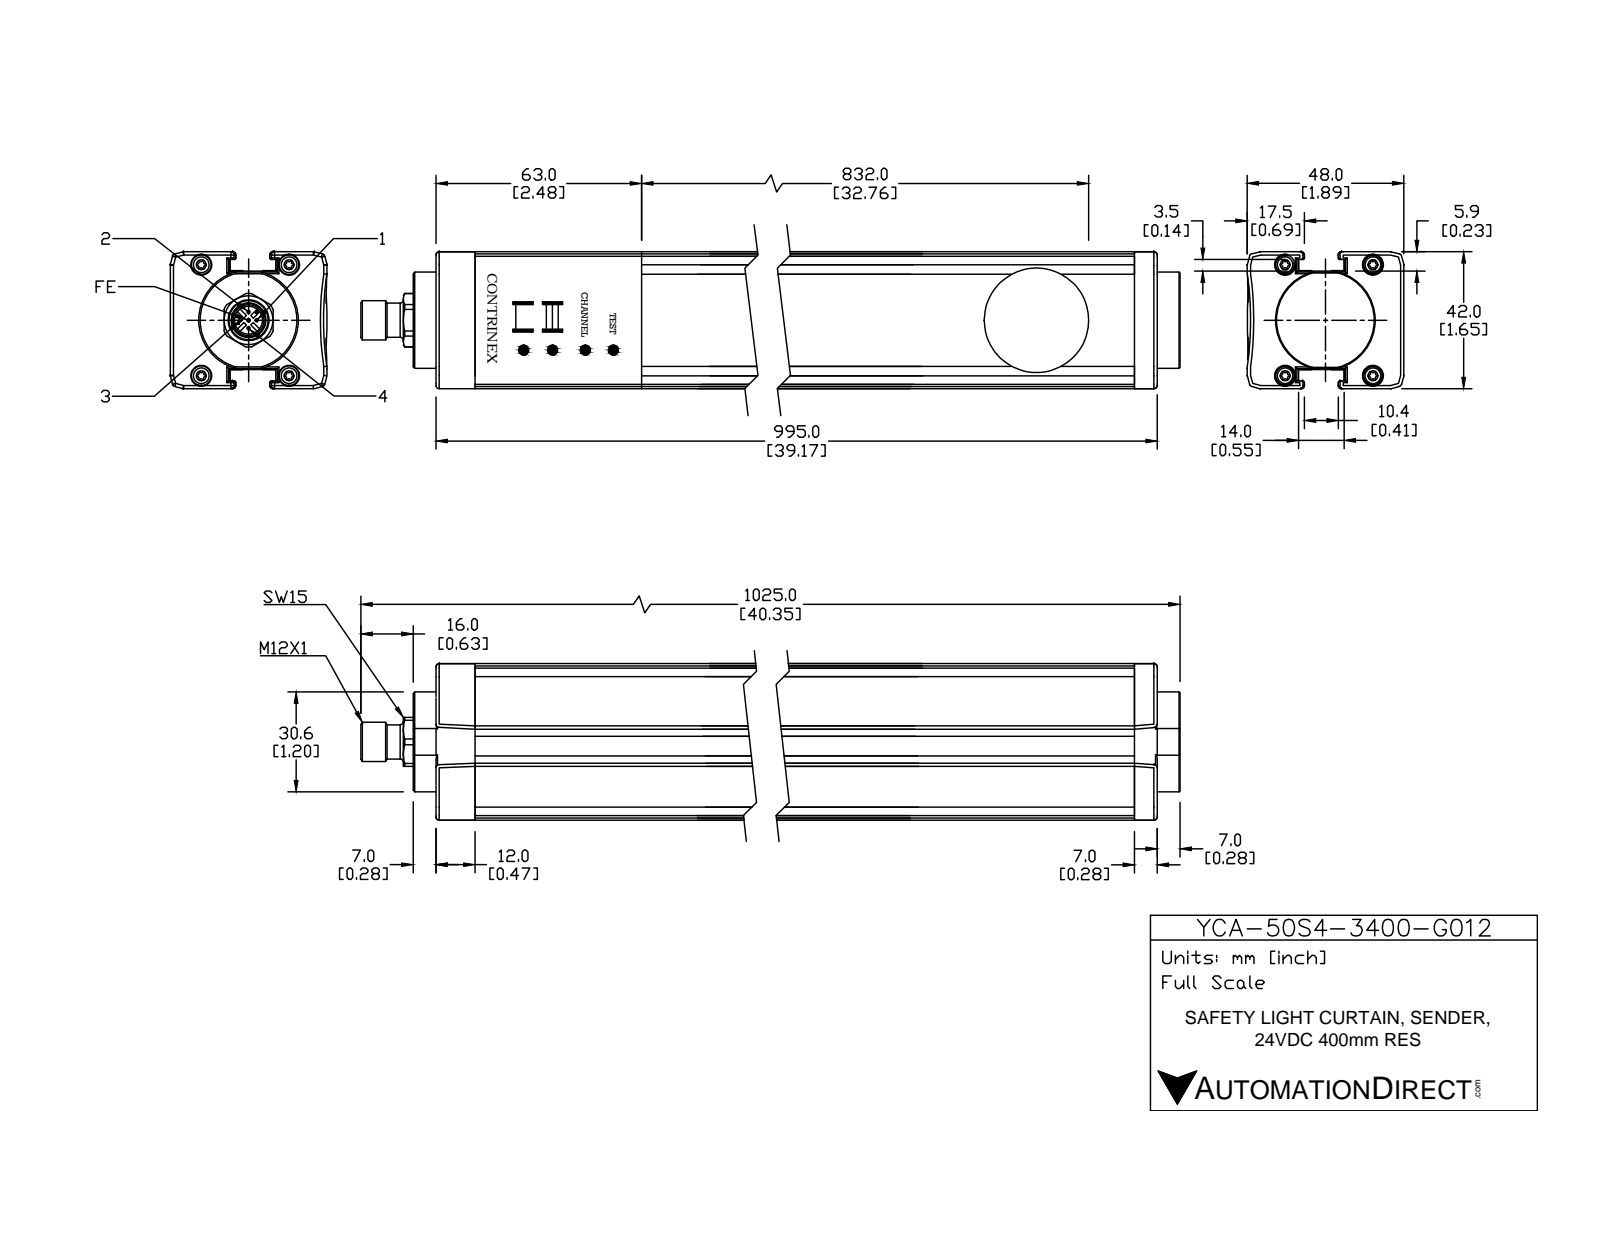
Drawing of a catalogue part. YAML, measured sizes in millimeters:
part_name: "YCA-50S4-3400-G012"
step_written_by: "SolidWorks 2016 (AUTOMOTIVE_DESIGN)"
units: millimeters
bodies: {solids: 18, faces: 454, planar: 221, cylindrical: 172, other: 61}
overall_size: [1025, 48, 42]
volume: 1794000
surface_area: 231840
round_holes:
  - {diameter: 6, count: 4}
  - {diameter: 1, count: 1}
  - {diameter: 8.5, count: 1}
  - {diameter: 32, count: 1}
round_bosses_or_shafts:
  - {diameter: 5.5, count: 4}
  - {diameter: 1, count: 4}
  - {diameter: 30.6, count: 1}
  - {diameter: 12, count: 1}
  - {diameter: 10.5, count: 1}
partial_cylinders:
  - {radius: 1, count: 52}
  - {radius: 0.5, count: 4}
  - {radius: 8.2, count: 1}
  - {radius: 100, count: 1}
face_to_face_distances: [42, 5.8, 36.2, 29.4, 1, 6.8, 35.2, 30.4, 14, 17.2]
hole_center_spacings: [21.04, 22.34, 26.9, 34, 43.35]
